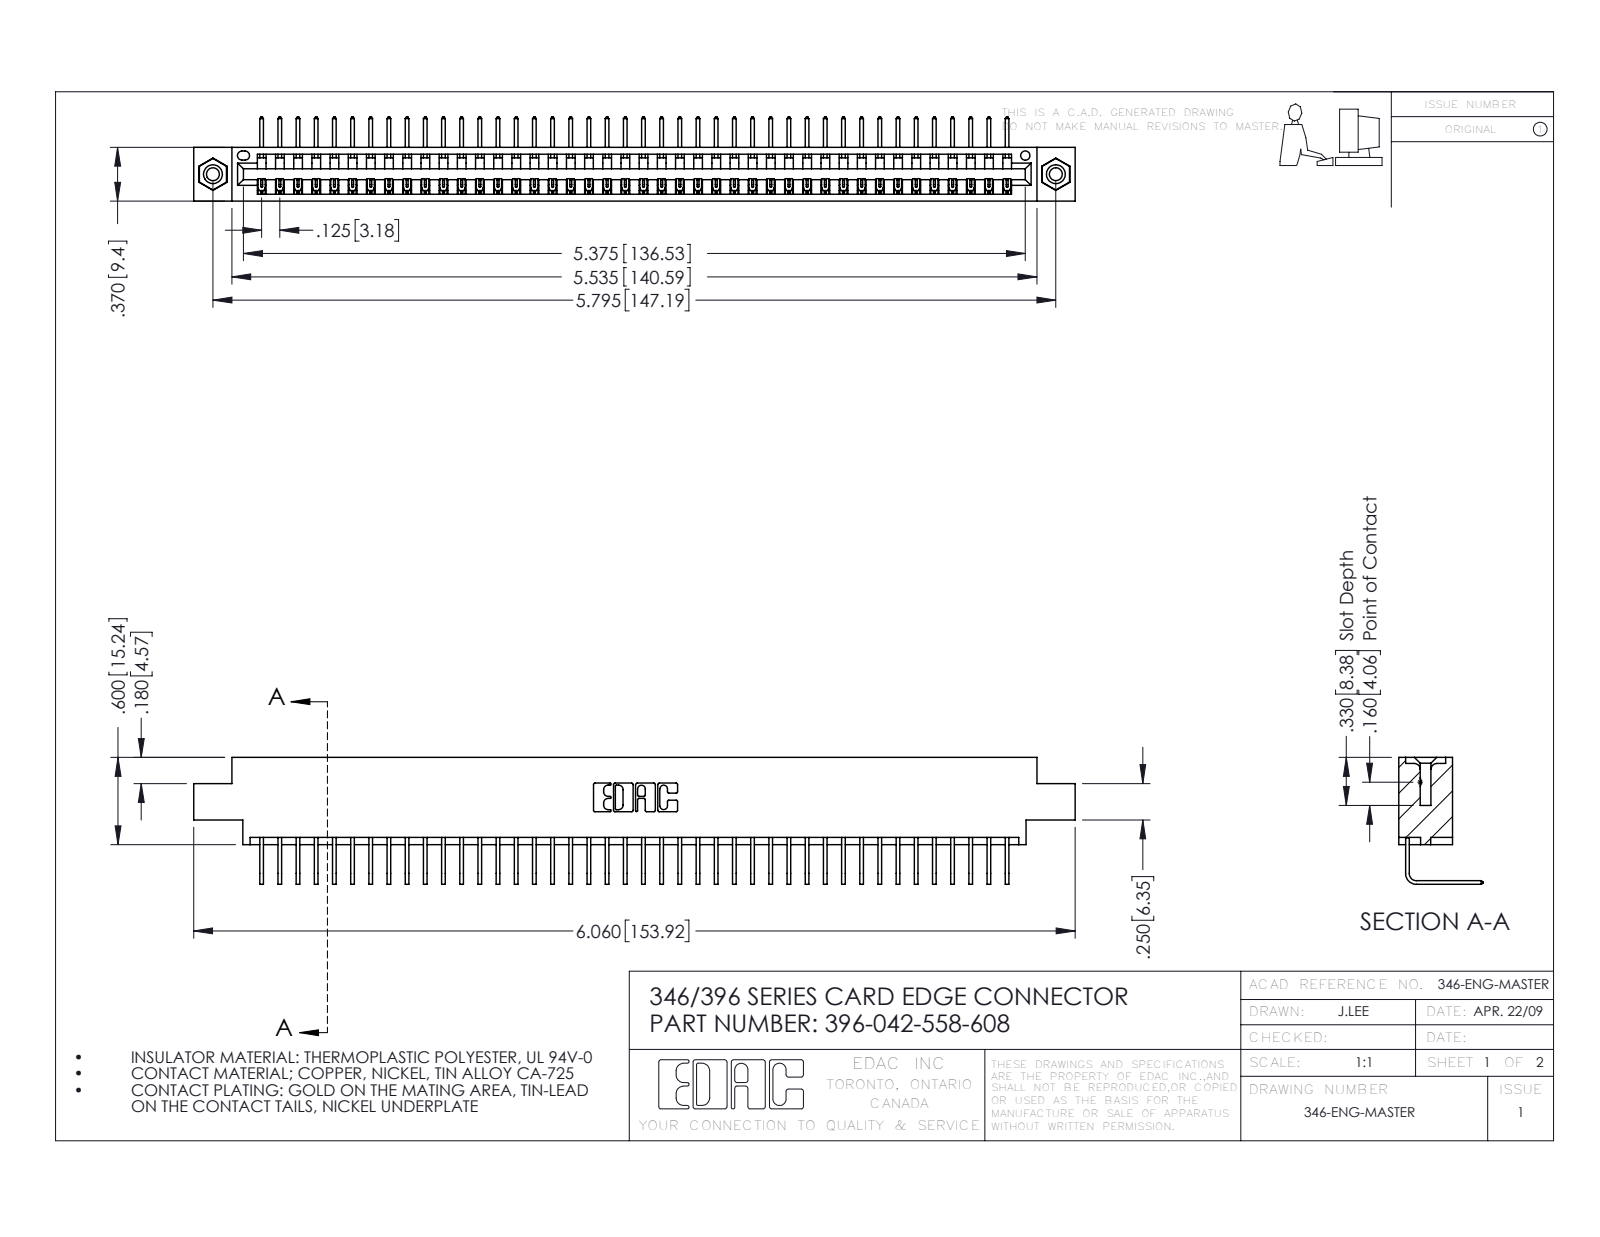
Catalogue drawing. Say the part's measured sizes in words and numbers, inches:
The part is named "346 Part_0.170 Offset - 0.156 Dia-TI; 345-292-001_558 Tail - 2; 345-250-001_345-250-003-102; 396-042-558-608". Its 3-D file was written by "SolidWorks 2016 (CONFIG_CONTROL_DESIGN)". It is 45 solids with 2706 faces: 1876 planar, 814 cylindrical and 16 other. Overall it measures 6.06 by 0.873 by 0.58 inches. Its volume is 0.898 cubic inches and its surface area 30.08 square inches. Round holes: 2 of diameter 0.089, 2 of diameter 0.125, 2 of diameter 0.156, 1 of diameter 0.064. Round bosses or shafts: 2 of diameter 0.155. Partial cylindrical surfaces (rounded edges, fillets, slot ends): 84 of radius 0.006, 22 of radius 0.01, 6 of radius 0.007, 6 of radius 0.031, 3 of radius 0.026, 2 of radius 0.031, 2 of radius 0.04, 1 of radius 0.014. The main face-to-face distances are 0.322, 0.048, 0.37, 0.25, 0.298, 0.025, 0.072, 0.222, 0.148, 0.1. The hole center spacings are 0.246, 5.586, 5.795.
